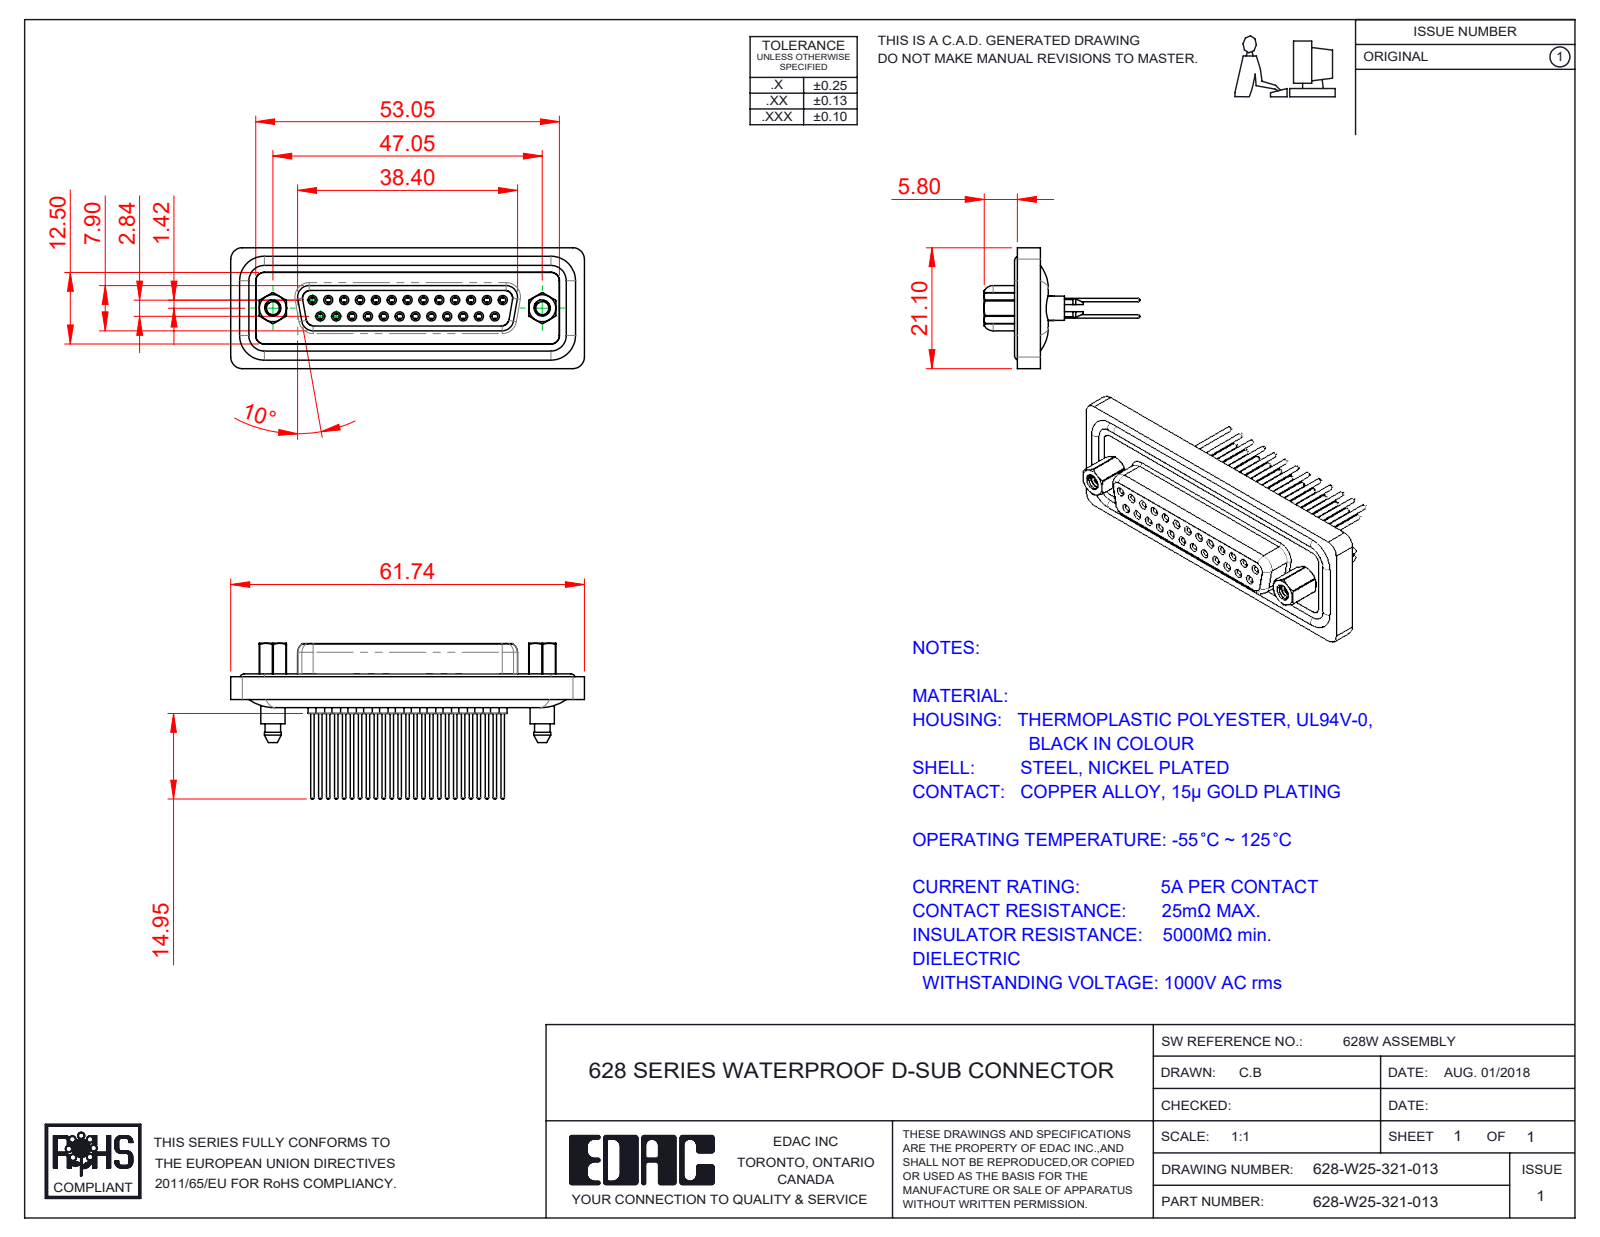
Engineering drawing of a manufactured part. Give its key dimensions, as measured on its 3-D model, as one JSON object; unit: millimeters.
{"part_name": "628W 4-40 Hex Standoff; 628-W25-321-013; 628W 4-40 Threaded Boardlock; 628W Contact Row 1_21 (+4 more)", "step_written_by": "SolidWorks 2020 (CONFIG_CONTROL_DESIGN)", "units": "millimeters", "bodies": {"solids": 33, "faces": 1894, "planar": 490, "cylindrical": 773, "other": 631}, "overall_size": [61.74, 27.2, 21.1], "volume_mm3": 7521, "surface_area_mm2": 13700, "round_holes": [[1, 25], [1.1, 25], [1.5, 25], [1.7, 25], [1.8, 25], [2, 25], [2.26, 2], [2.29, 2], [4, 2], [4.25, 2], [4.8, 2]], "round_bosses_or_shafts": [[1.6, 29], [2.2, 25], [0.6, 25], [1.5, 12], [5.4, 2], [4.9, 2], [2.79, 2], [4.8, 1]], "partial_cylinders_radius": [[1.5, 16], [2, 14], [1.35, 8], [1.6, 6], [0.5, 4], [0.9, 4], [1.75, 4], [2.7, 4]], "face_to_face_distances": [0.4, 1.8, 1.6, 2.9, 2.5, 1.1, 7.45, 13.65, 4.1, 6.2], "hole_center_spacings": [3.16, 2.77, 5.54, 8.31, 11.08, 13.85, 5.03, 5.04]}
